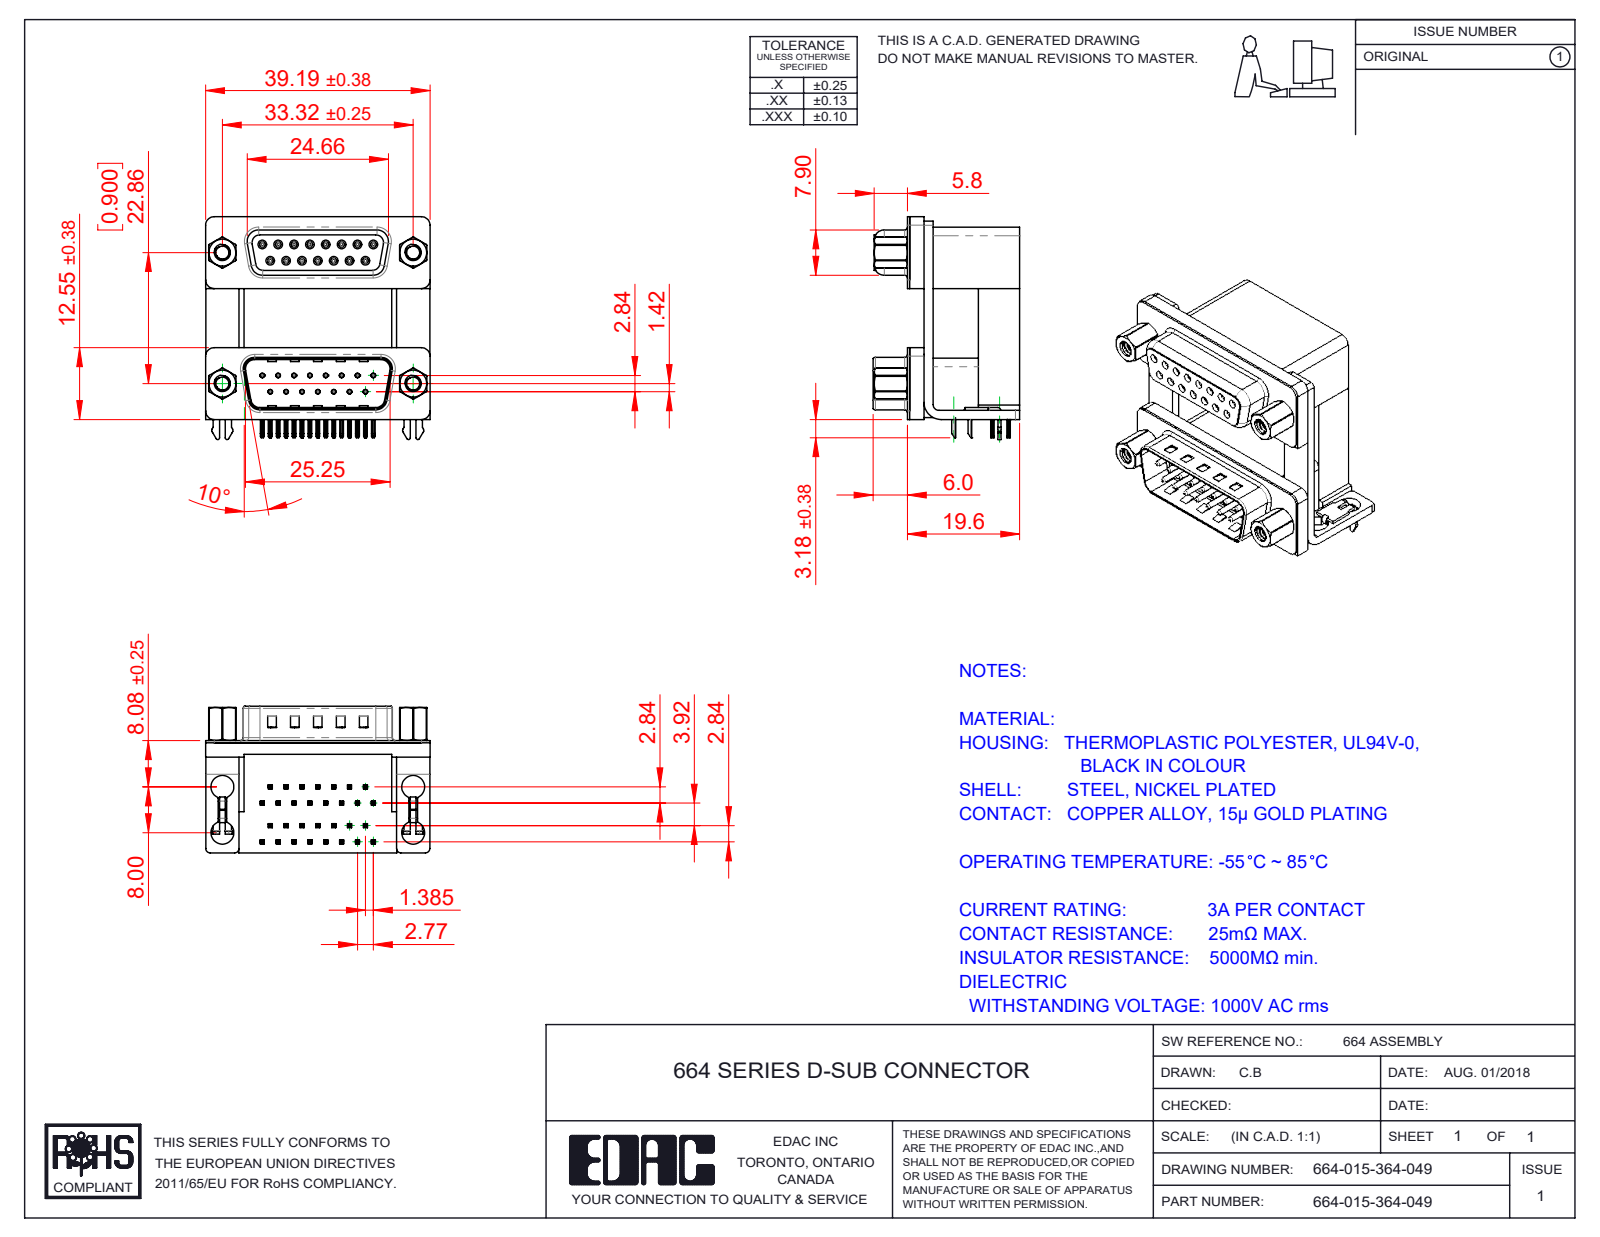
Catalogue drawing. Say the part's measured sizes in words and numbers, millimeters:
The part is named "664 Housing Upper_15 Contacts H; 664 4-40 Hex Standoff 5; 664 Contact Top Upper_H; 664 Contact Bottom Lower (+8 more)". Its 3-D file was written by "SolidWorks 2020 (CONFIG_CONTROL_DESIGN)". It is 47 solids with 4272 faces: 2137 planar, 1188 cylindrical and 947 other. Overall it measures 39.19 by 38.91 by 25.6 millimeters. Its volume is 16 358 cubic millimeters and its surface area 18 676 square millimeters. Round holes: 30 of diameter 0.8, 15 of diameter 0.35, 15 of diameter 0.9, 8 of diameter 4, 4 of diameter 2.26, 4 of diameter 2.29, 4 of diameter 3.5, 4 of diameter 4.8, 4 of diameter 5. Round bosses or shafts: 15 of diameter 1.2, 15 of diameter 0.75, 4 of diameter 4.9, 4 of diameter 4.75, 4 of diameter 3.9, 4 of diameter 2.79. Partial cylindrical surfaces (rounded edges, fillets, slot ends): 121 of radius 0.1, 66 of radius 0.25, 60 of radius 0.15, 30 of radius 0.12, 30 of radius 0.35, 16 of radius 0.5, 16 of radius 1.5, 15 of radius 0.34. The main face-to-face distances are 0.4, 19.2, 12, 7.2, 16.7, 9.5, 2.5, 12.4, 2.19, 22.86. The hole center spacings are 3.16, 2.77, 23.03, 5.54, 23.52, 8.31, 22.86, 24.32.
